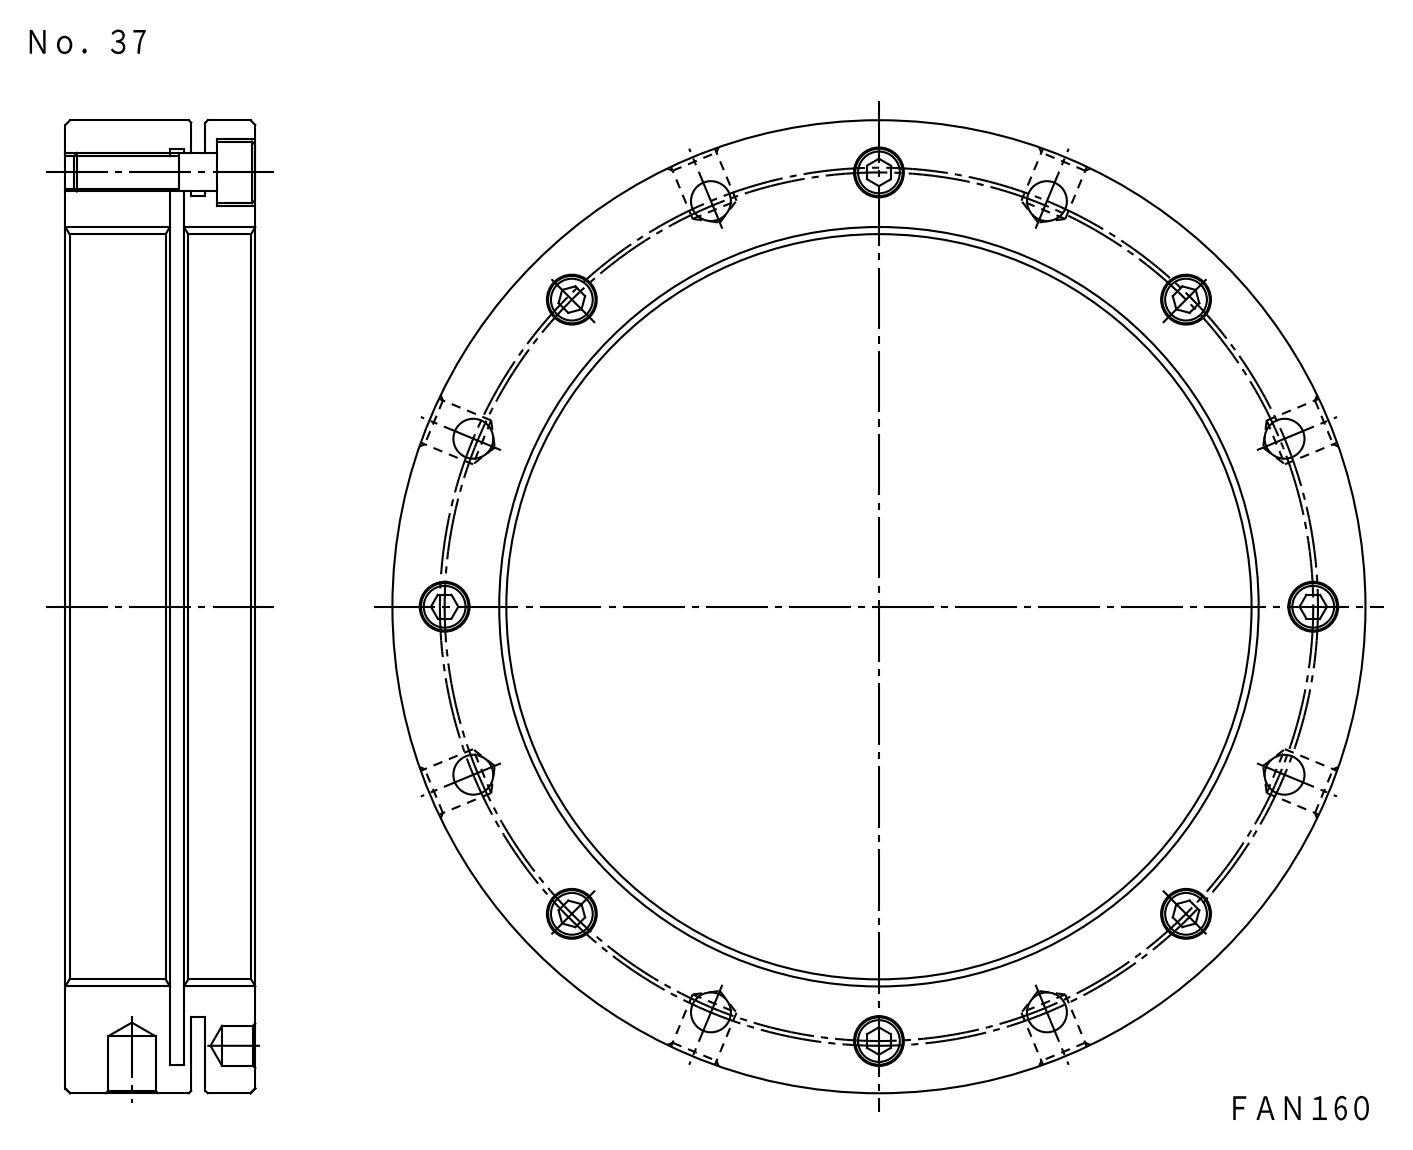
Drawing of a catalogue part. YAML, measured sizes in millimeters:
part_name: "FKD FAN160; M8X30_default"
step_written_by: "SolidWorks 2012 (CONFIG_CONTROL_DESIGN)"
units: millimeters
bodies: {solids: 9, faces: 266, planar: 94, cylindrical: 140, other: 32}
overall_size: [205, 205, 40]
volume: 450098
surface_area: 130021
round_holes:
  - {diameter: 6.65, count: 8}
  - {diameter: 8.4, count: 8}
  - {diameter: 8.6, count: 8}
  - {diameter: 10, count: 8}
  - {diameter: 14, count: 8}
  - {diameter: 160, count: 1}
  - {diameter: 193, count: 1}
round_bosses_or_shafts:
  - {diameter: 13, count: 8}
  - {diameter: 8, count: 8}
  - {diameter: 205, count: 1}
  - {diameter: 173, count: 1}
face_to_face_distances: [3, 4.5, 40, 26.5, 29.5, 13.5, 10.5, 22, 7.5, 18]
hole_center_spacings: [35.91, 102.23, 152.99, 180.47, 70.03, 70.8, 91.5, 92.5]
